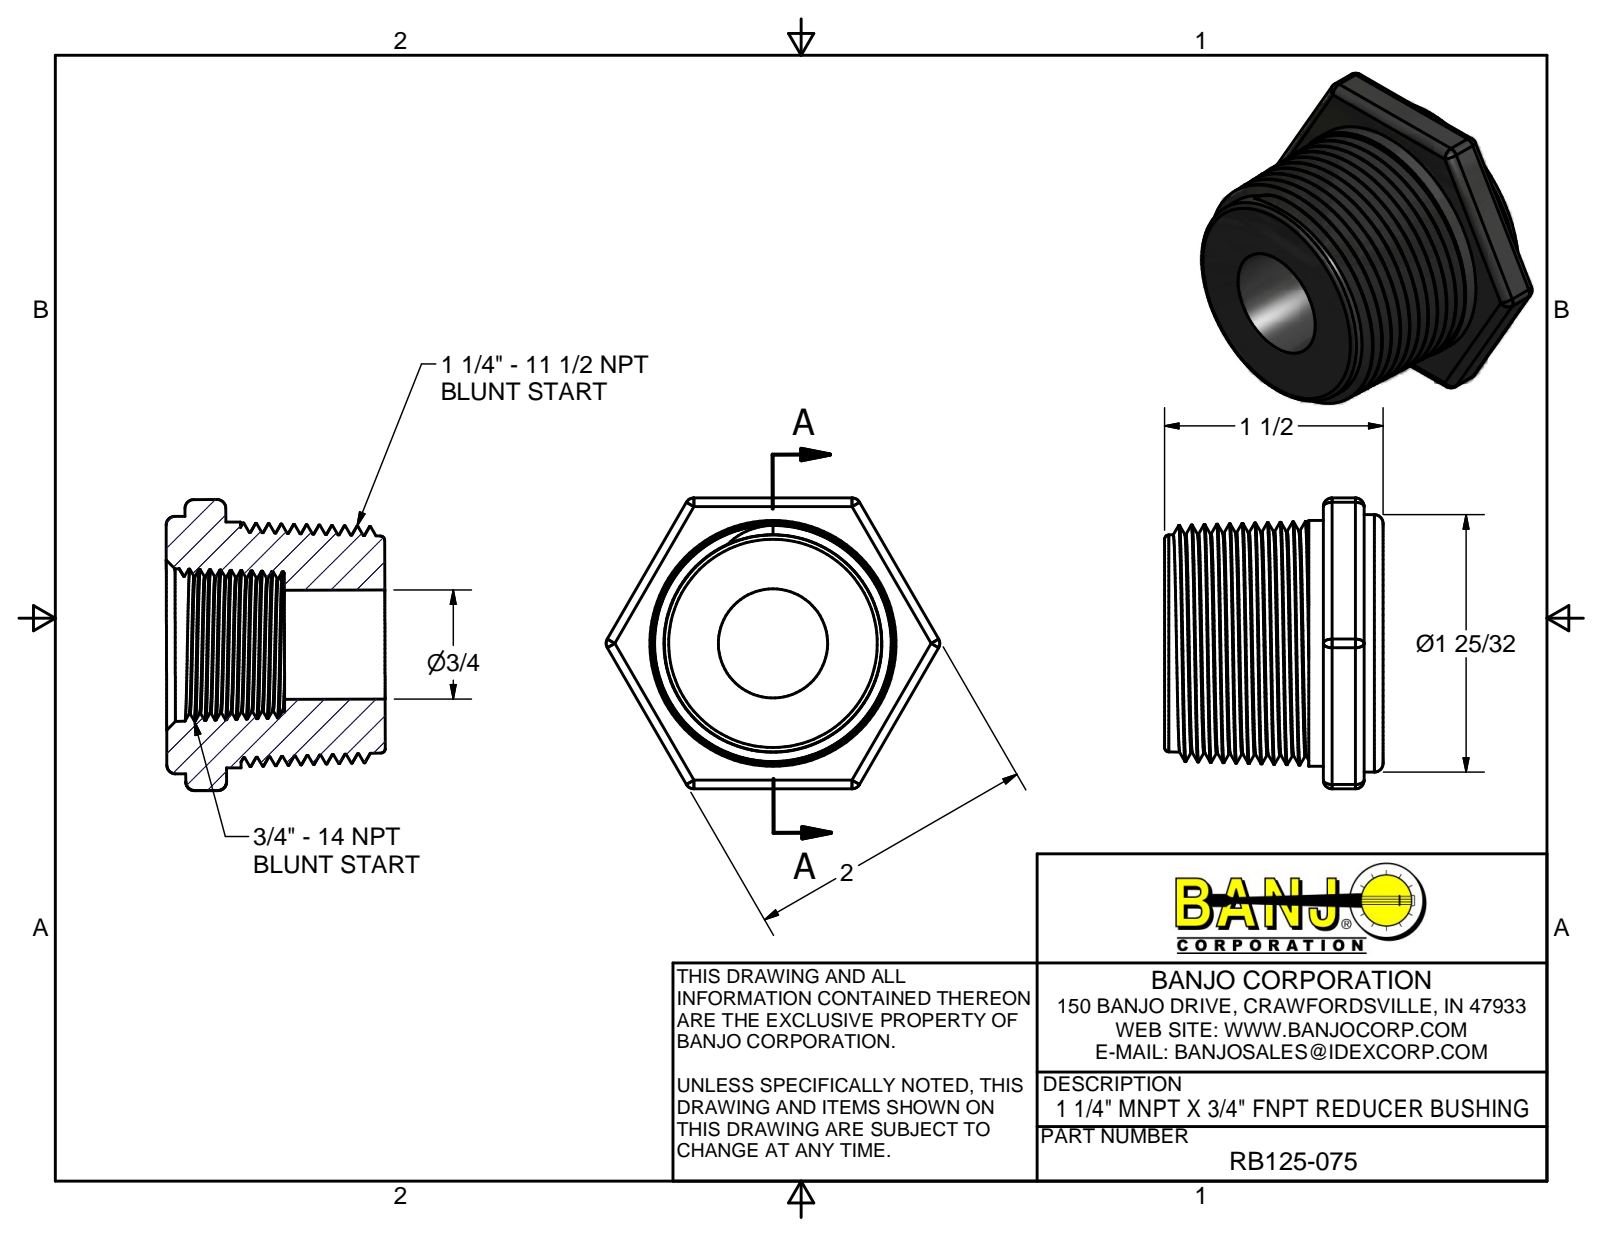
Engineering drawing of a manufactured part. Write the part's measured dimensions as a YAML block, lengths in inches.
part_name: "RB125-075"
step_written_by: "Autodesk Inventor 2014 (AUTOMOTIVE_DESIGN)"
units: inches
bodies: {solids: 1, faces: 82, planar: 12, cylindrical: 23, other: 47}
overall_size: [2.291, 2, 1.5]
volume: 2.499
surface_area: 22.57
round_holes:
  - {diameter: 0.75, count: 1}
round_bosses_or_shafts:
  - {diameter: 1.77, count: 1}
  - {diameter: 1.69, count: 1}
partial_cylinders:
  - {radius: 0.06, count: 18}
  - {radius: 0.313, count: 1}
  - {radius: 0.437, count: 1}
face_to_face_distances: [1.5, 0.41, 1.09, 0.13, 0.28, 1.37, 2, 0.81, 0.68, 0.4]
